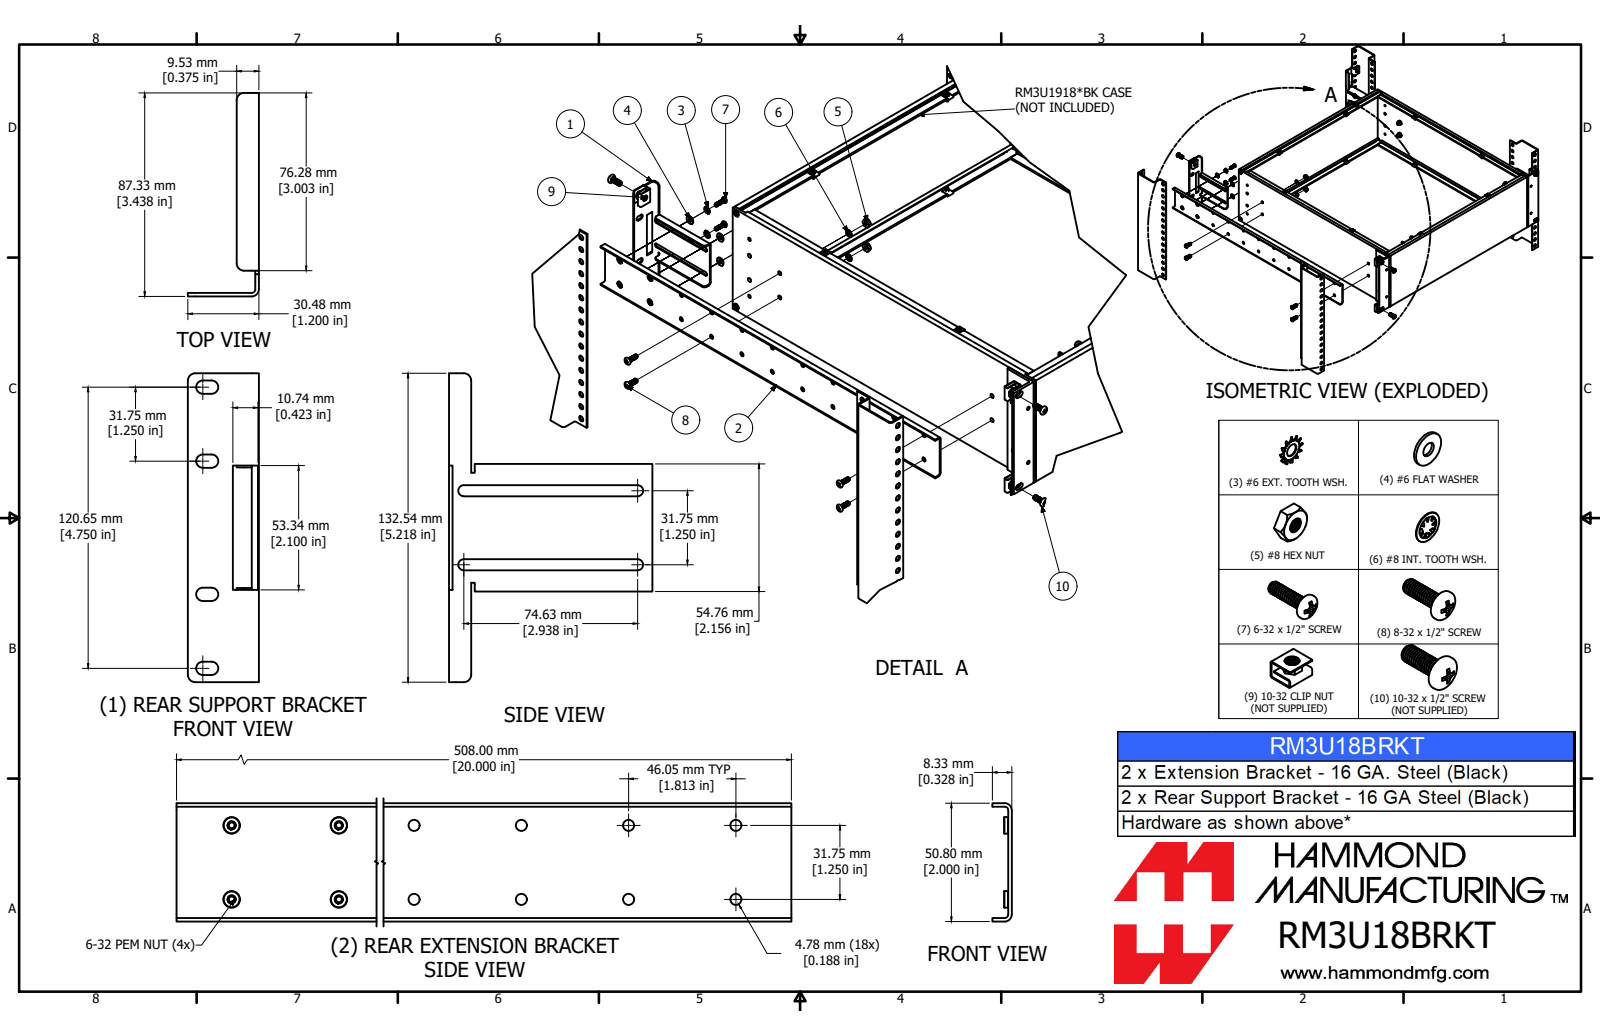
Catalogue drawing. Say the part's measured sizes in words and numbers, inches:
The part is named "RM3U18BRKT". Its 3-D file was written by "SolidWorks 2021 (AUTOMOTIVE_DESIGN)". It is 6 solids with 734 faces: 494 planar, 208 cylindrical and 32 other. Overall it measures 20.307 by 5.218 by 1.2 inches. Its volume is 3.74 cubic inches and its surface area 131.8 square inches. Round holes: 22 of diameter 0.188, 4 of diameter 0.097, 4 of diameter 0.138. Round bosses or shafts: 4 of diameter 0.28. Partial cylindrical surfaces (rounded edges, fillets, slot ends): 7 of radius 0.112, 6 of radius 0.125, 5 of radius 0.06, 5 of radius 0.12, 4 of radius 0.094, 4 of radius 0.106, 1 of radius 0.113. The main face-to-face distances are 0.06, 1.94, 0.12, 2, 1.88, 0.078, 2.018, 0.388, 0.328, 0.268. The hole center spacings are 1.813, 2.202, 3.626, 3.835, 5.439, 5.581, 7.252, 7.359.
